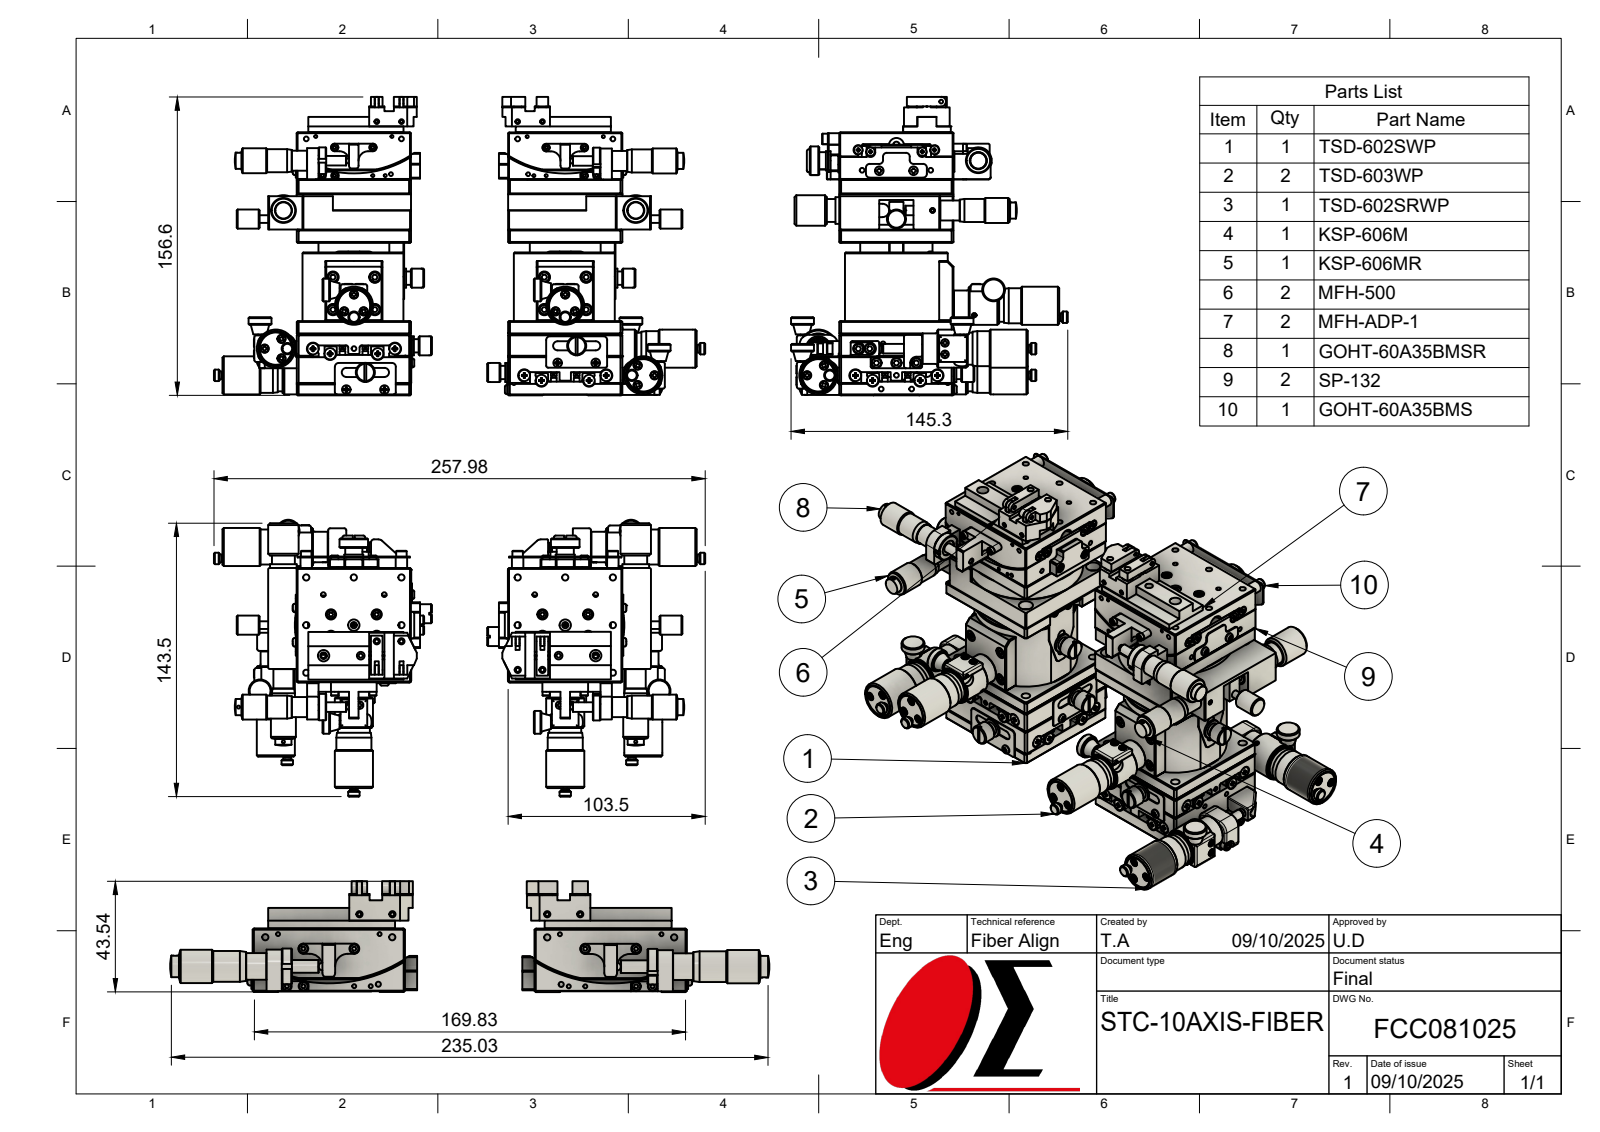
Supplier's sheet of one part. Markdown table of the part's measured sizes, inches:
| quantity | value |
| --- | --- |
| part name | STC-12AXIS-FIBER; TSD-602SWP; TSD-602SWP-C1-S08; TSD-602SWP-C1-S10 (+8 more) |
| STEP written by | Autodesk Translation Framework v14.17.0.0 (AUTOMOTIVE_DESIGN) |
| units | inches |
| bodies | 137 solids, 9533 faces (5340 planar, 2882 cylindrical, 1311 other) |
| overall size | 10.157 × 6.165 × 5.72 |
| volume | 52.12 in³ |
| surface area | 677.1 in² |
| round holes (diameter × count) | 0.097 × 100, 0.071 × 72, 0.128 × 65, 0.062 × 61, 0.236 × 35, 0.087 × 34, 0.118 × 32, 0.062 × 30, 0.083 × 28, 0.315 × 28, 0.177 × 26, 0.094 × 21 |
| round bosses / shafts (diameter × count) | 0.157 × 78, 0.079 × 73, 0.177 × 45, 0.118 × 33, 0.217 × 32, 0.236 × 28, 0.138 × 20, 0.276 × 19 |
| partial cylindrical surfaces (radius × count) | 0.039 × 267, 0.012 × 128, 0.079 × 122, 0.031 × 76, 0.118 × 52, 0.128 × 28, 0.02 × 22, 0.197 × 22 |
| main face-to-face distances | 2.362, 1.024, 2.913, 2.165, 0.748, 0.276, 0.02, 3.189, 0.244, 0.551 |
| hole center spacings | 0.236, 0.413, 0.498, 1.457, 1.478, 1.953, 2.398, 0.138 |
